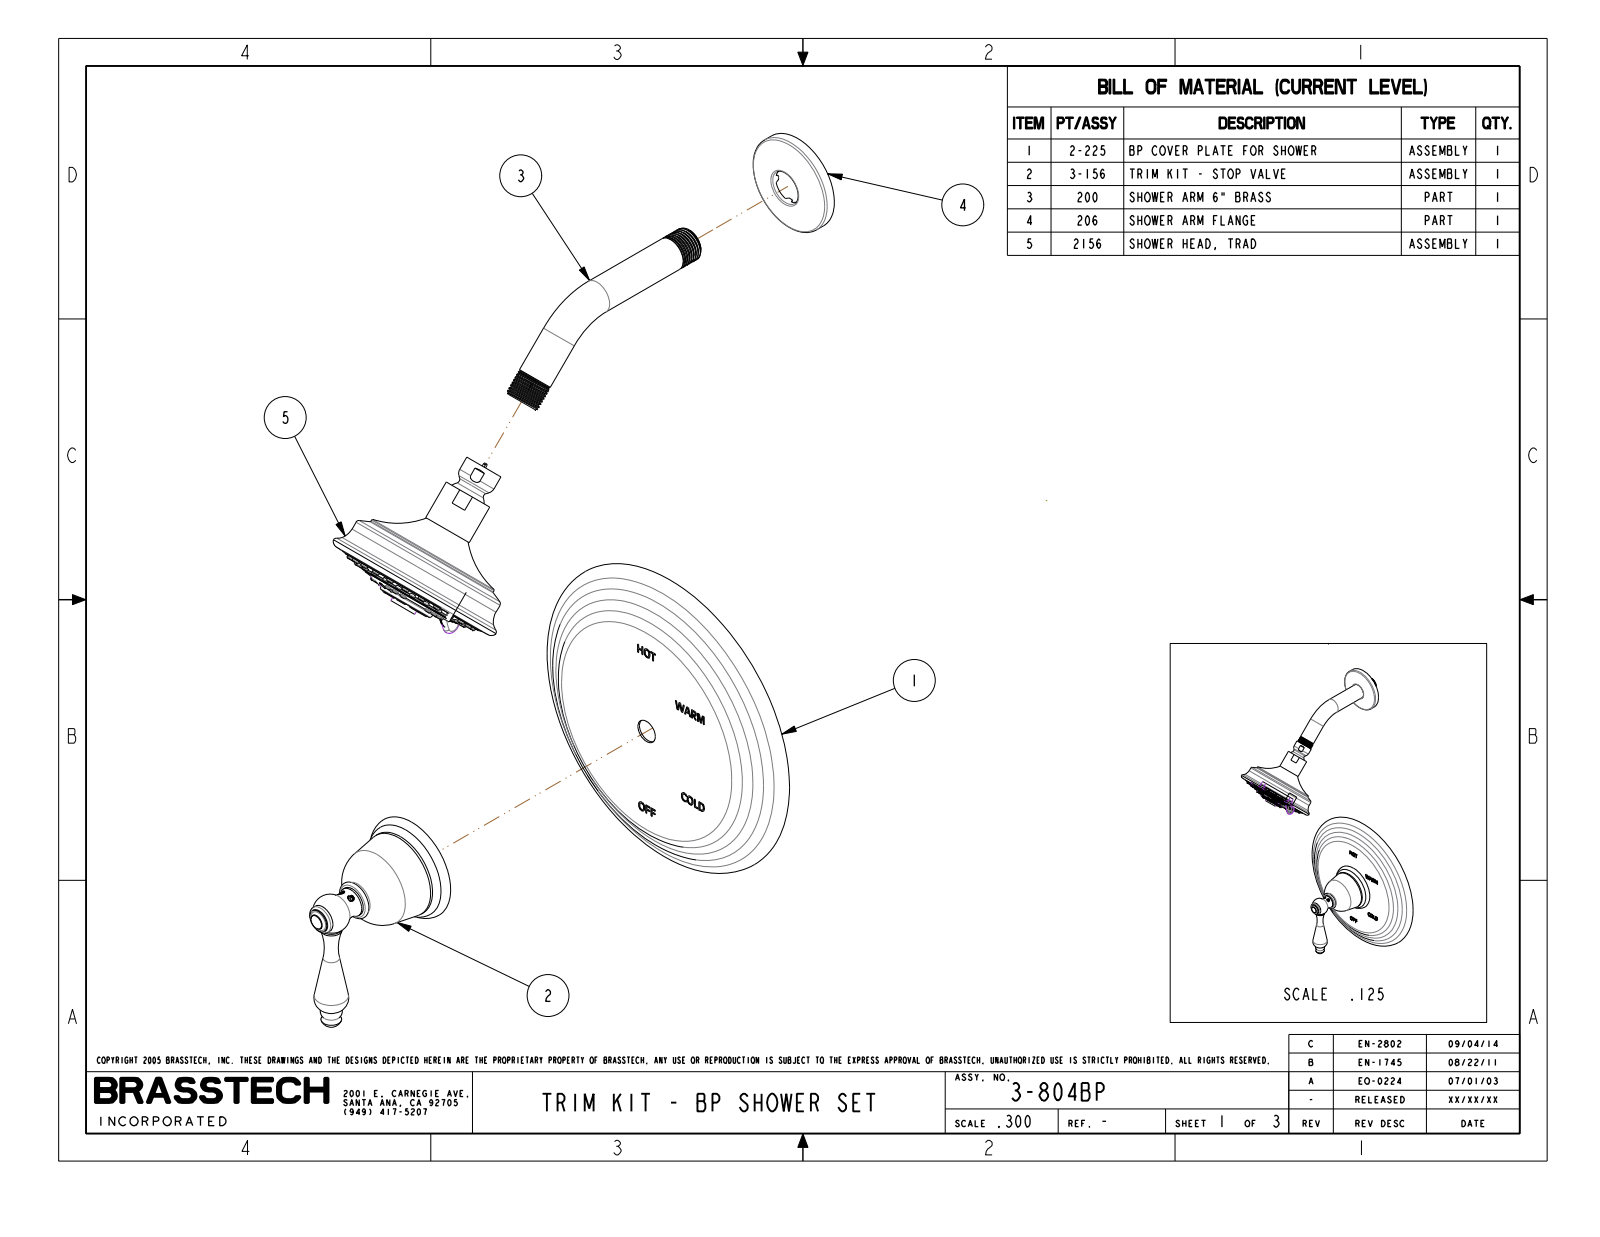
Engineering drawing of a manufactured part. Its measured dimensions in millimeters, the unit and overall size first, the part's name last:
Units: millimetres
Overall size (bounding box): 458.9 × 229.1 × 196.9
Round holes (diameter × count): ⌀1.1 ×32, ⌀2.5 ×15, ⌀1.5 ×12, ⌀2 ×8, ⌀2.4 ×8, ⌀4.7 ×8, ⌀3 ×7, ⌀3.8 ×3, ⌀6.4 ×3, ⌀7 ×3, ⌀3.3 ×2, ⌀6.8 ×2
Round bosses / shafts (diameter × count): ⌀3.6 ×39, ⌀4.2 ×23, ⌀8 ×3, ⌀6.2 ×3, ⌀20.7 ×2, ⌀19.5 ×2, ⌀16 ×2, ⌀5.8 ×2
Partial cylindrical surfaces — rounded edges, fillets, slot ends (radius × count): R0.5 ×52, R0.3 ×29, R2.1 ×15, R0.2 ×14, R2 ×10, R0.8 ×8, R2.2 ×8, R18.9 ×5
Main face-to-face distances: 1.3, 2.5, 5.3, 7.3, 7.8, 4.8, 2, 2.7, 2.6, 0.5
Hole centre spacings: 9.6, 7, 10.7, 9.4, 15.4, 6.1, 19.9, 20
Volume: 252 700 mm³ · Surface area: 385 200 mm²
Bodies: 46 solids, 7268 faces (3247 planar, 1612 cylindrical, 2409 other)
Part name (STEP PRODUCT): 206; 200; 80096; 50784 (+8 more)
STEP written by: PRO/ENGINEER BY PARAMETRIC TECHNOLOGY CORPORATION, 2013150 (CONFIG_CONTROL_DESIGN)
